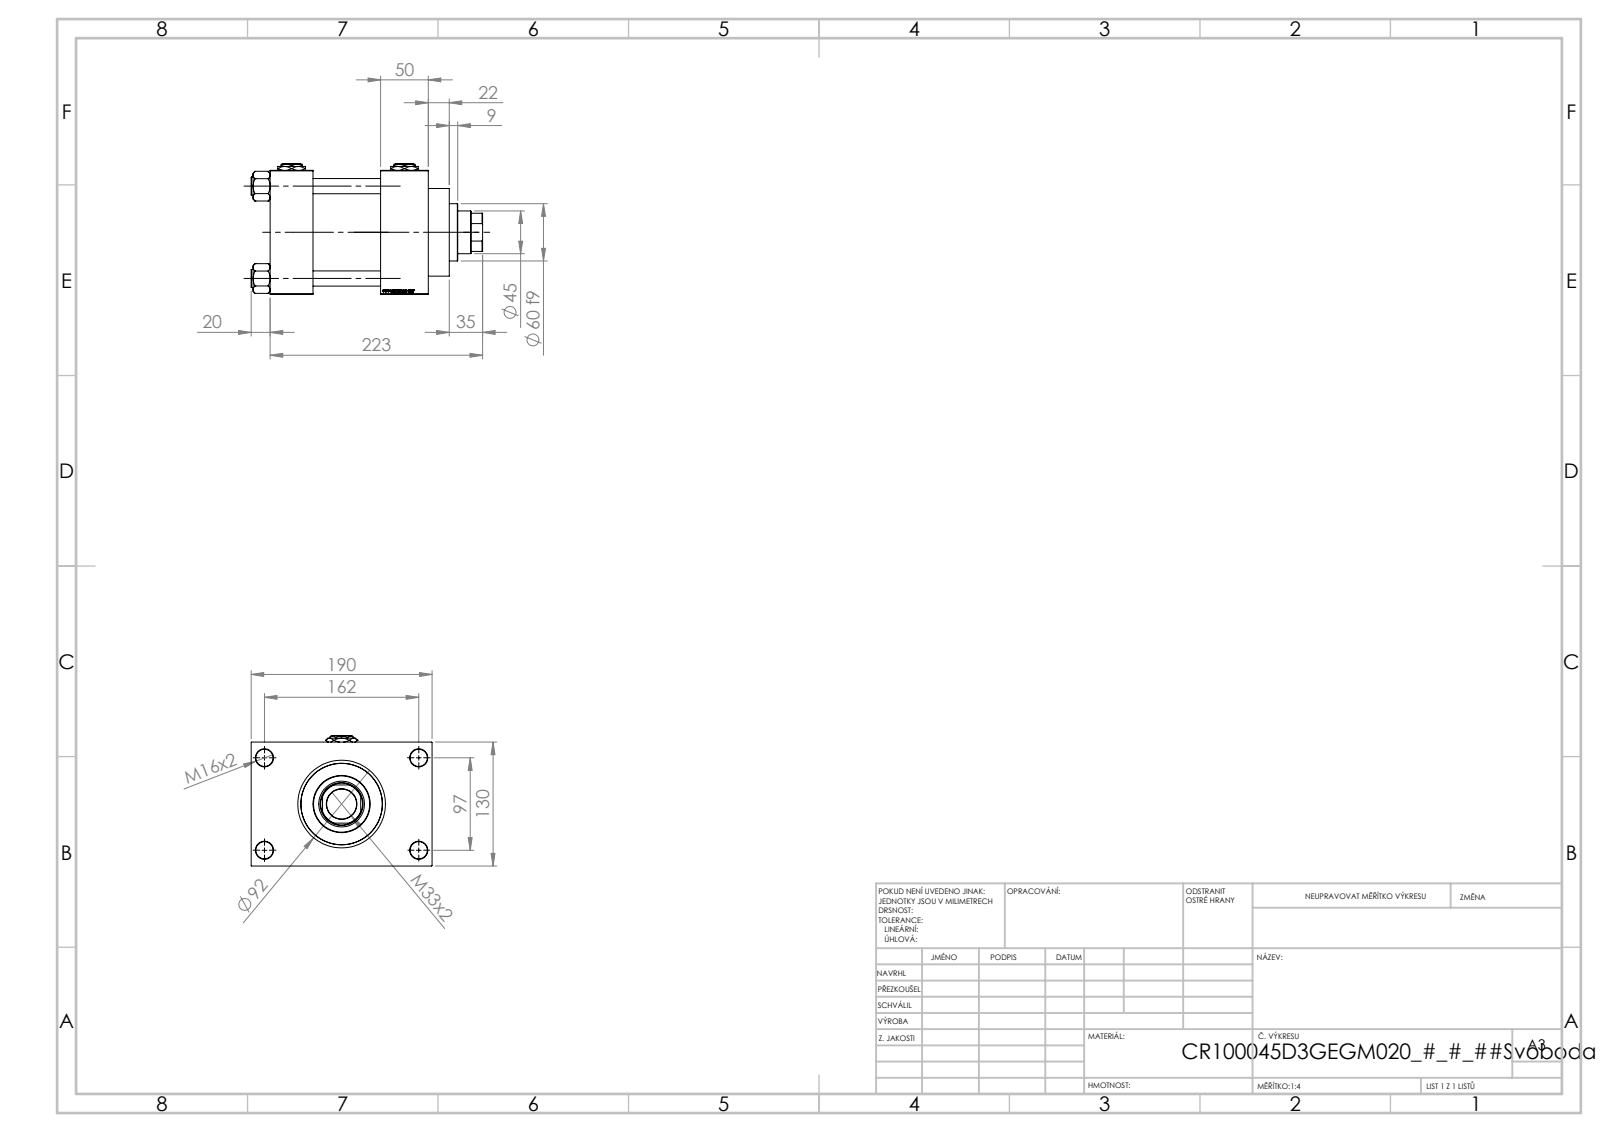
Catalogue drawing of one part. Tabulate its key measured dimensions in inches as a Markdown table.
| quantity | value |
| --- | --- |
| part name | V215CR_VCP_D; V215_VC_A; V215CR_D_Body; Zatka_pro_OIL_PORT (+2 more) |
| STEP written by | SolidWorks 2019 (CONFIG_CONTROL_DESIGN) |
| units | inches |
| bodies | 13 solids, 1253 faces (593 planar, 100 cylindrical, 560 other) |
| overall size | 9.567 × 7.48 × 5.394 |
| volume | 158.2 in³ |
| surface area | 556.9 in² |
| round holes (diameter × count) | 0.63 × 4, 0.709 × 4, 0.276 × 2, 1.041 × 2, 1.378 × 2, 1.24 × 1, 1.772 × 1, 1.89 × 1, 2.992 × 1, 3.366 × 1, 3.937 × 1 |
| round bosses / shafts (diameter × count) | 0.748 × 4, 4.173 × 1, 3.622 × 1, 2.362 × 1 |
| partial cylindrical surfaces (radius × count) | 0.866 × 1 |
| main face-to-face distances | 5.118, 1.772, 4.567, 2.795, 6.535, 4.764, 1.969, 6.299, 1.181, 0.787 |
| hole center spacings | 1.281, 2.698, 3.717, 3.815, 4.026, 5.096, 6.367, 3.819 |
